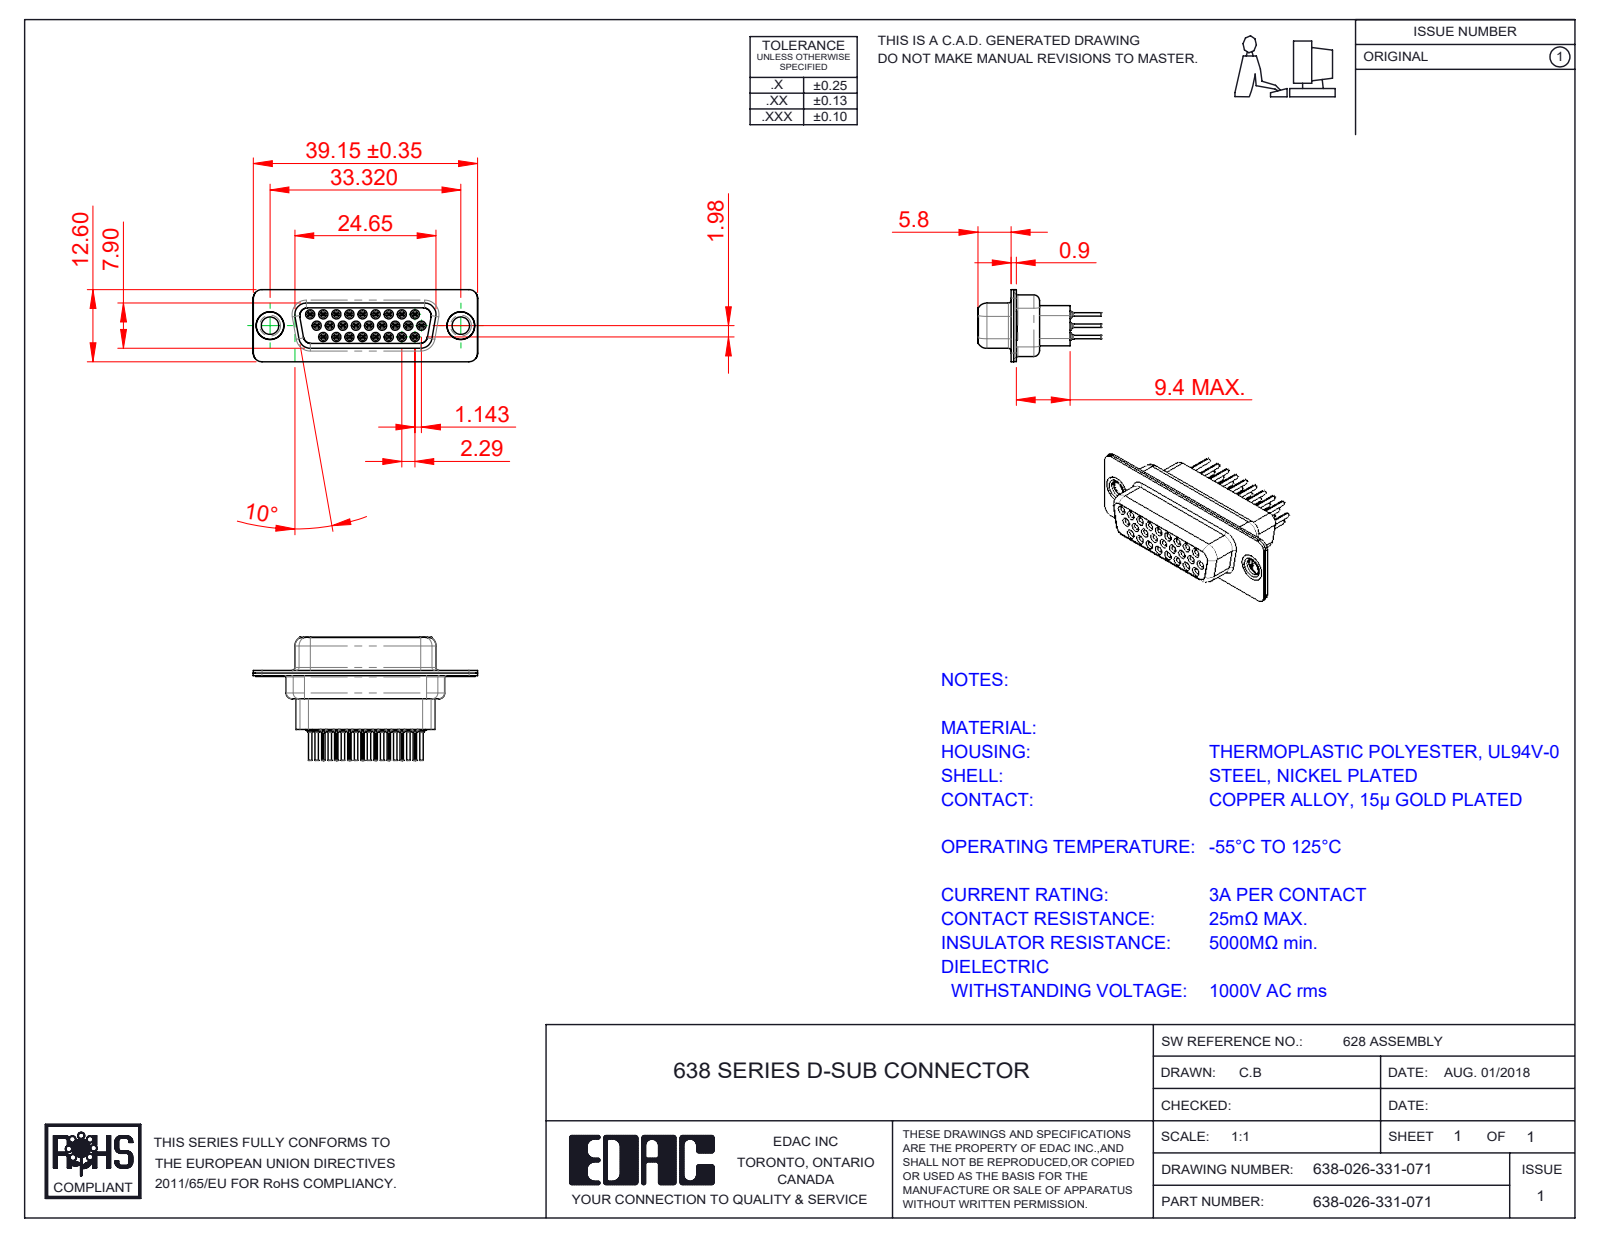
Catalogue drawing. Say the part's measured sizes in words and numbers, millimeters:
The part is named "638 Thru Hole Rivet; 638 Shell Front_26 Contacts; 638 Shell Rear_26 Contacts; 638 Contact Row 1_31 (+4 more)". Its 3-D file was written by "SolidWorks 2020 (CONFIG_CONTROL_DESIGN)". It is 31 solids with 3451 faces: 873 planar, 979 cylindrical and 1599 other. Overall it measures 39.19 by 21.5 by 12.6 millimeters. Its volume is 2 598 cubic millimeters and its surface area 9 726 square millimeters. Round holes: 26 of diameter 0.2, 26 of diameter 0.8, 26 of diameter 1, 26 of diameter 1.1, 26 of diameter 1.6, 26 of diameter 1.7, 26 of diameter 1.8, 2 of diameter 3.05, 2 of diameter 4, 2 of diameter 4.05, 2 of diameter 4.85. Round bosses or shafts: 26 of diameter 2, 26 of diameter 1.5, 26 of diameter 1.2, 26 of diameter 0.6, 2 of diameter 5, 2 of diameter 4.95, 2 of diameter 4.8, 2 of diameter 3.55. Partial cylindrical surfaces (rounded edges, fillets, slot ends): 52 of radius 0.1, 20 of radius 1.5, 18 of radius 0.28, 12 of radius 2, 8 of radius 1.55, 5 of radius 1.35, 4 of radius 0.25, 4 of radius 0.5. The main face-to-face distances are 0.45, 0.4, 6.6, 1.43, 8.88, 0.9, 7, 2.28, 6.2, 5.8. The hole center spacings are 3.96, 2.28, 4.57, 6.05, 2.29, 8.24, 6.86, 10.48.
